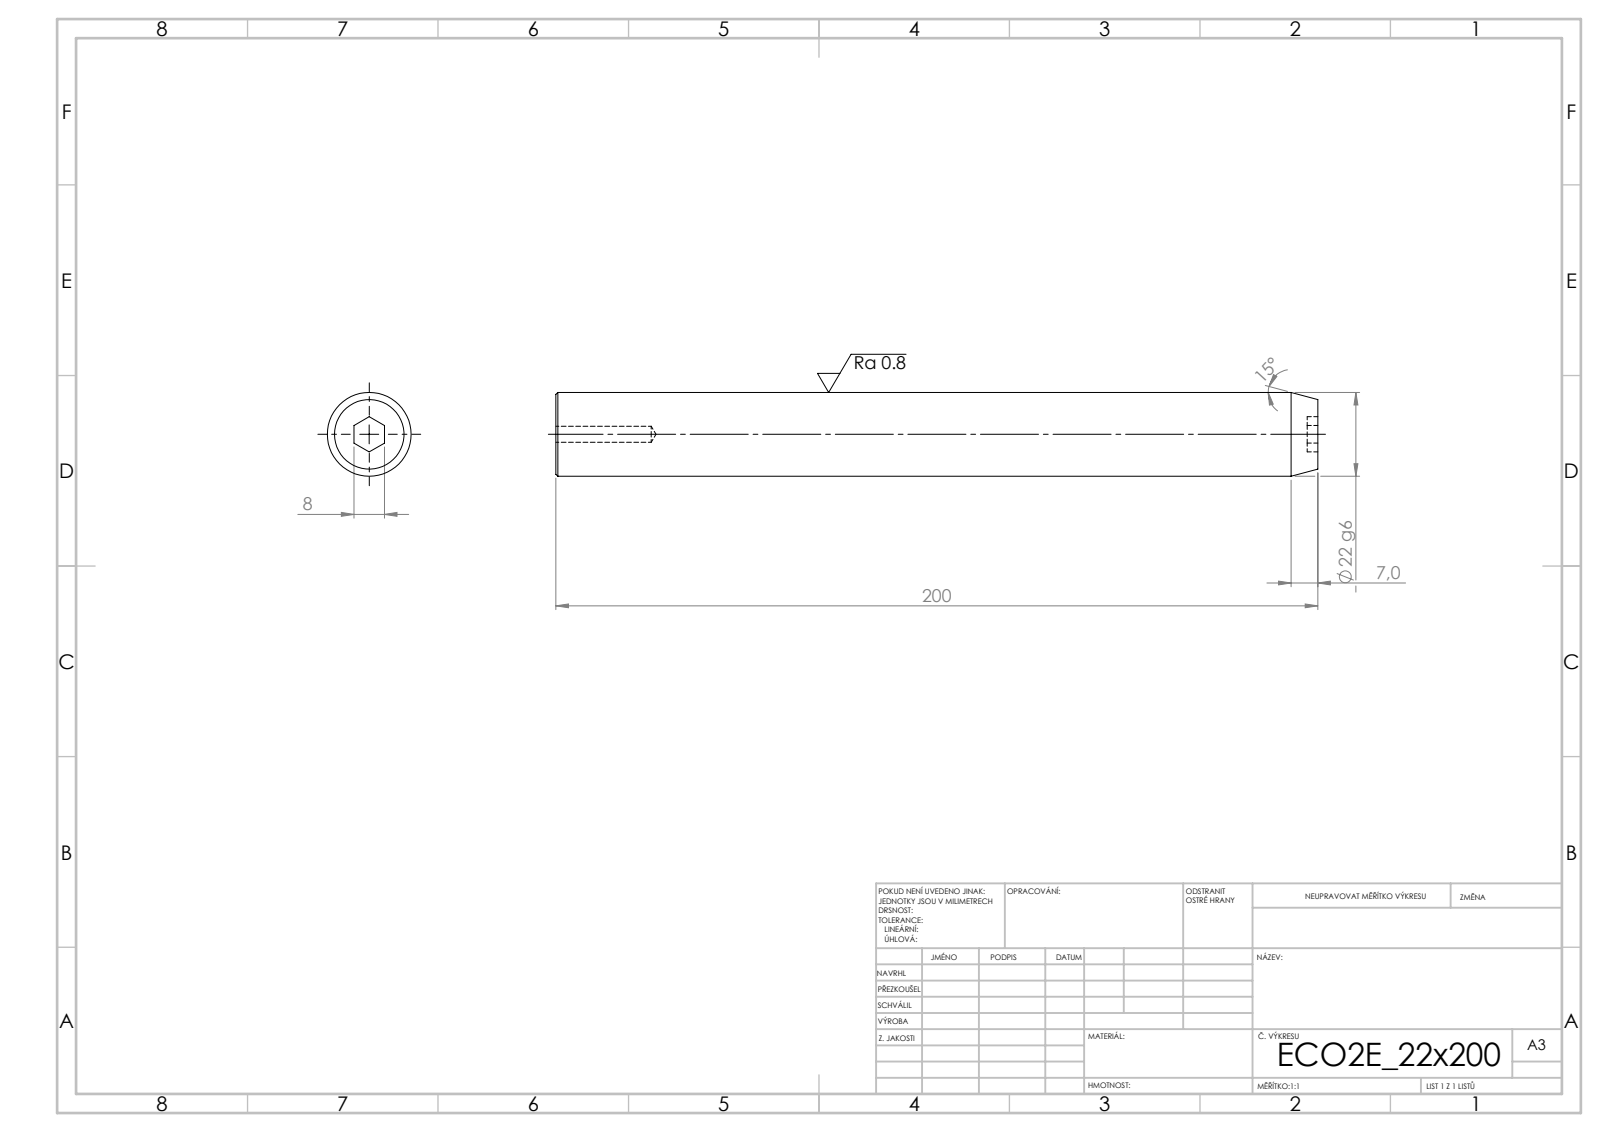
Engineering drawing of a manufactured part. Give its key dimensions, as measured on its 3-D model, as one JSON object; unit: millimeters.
{"step_written_by": "SolidWorks 2019 (CONFIG_CONTROL_DESIGN)", "units": "millimeters", "bodies": {"solids": 1, "faces": 19, "planar": 9, "cylindrical": 4, "other": 6}, "overall_size": [200, 22, 22], "volume_mm3": 75083, "surface_area_mm2": 14828, "round_holes": [[4.2, 1]], "round_bosses_or_shafts": [[22, 1]], "face_to_face_distances": [200, 2.8, 197.2, 8]}
